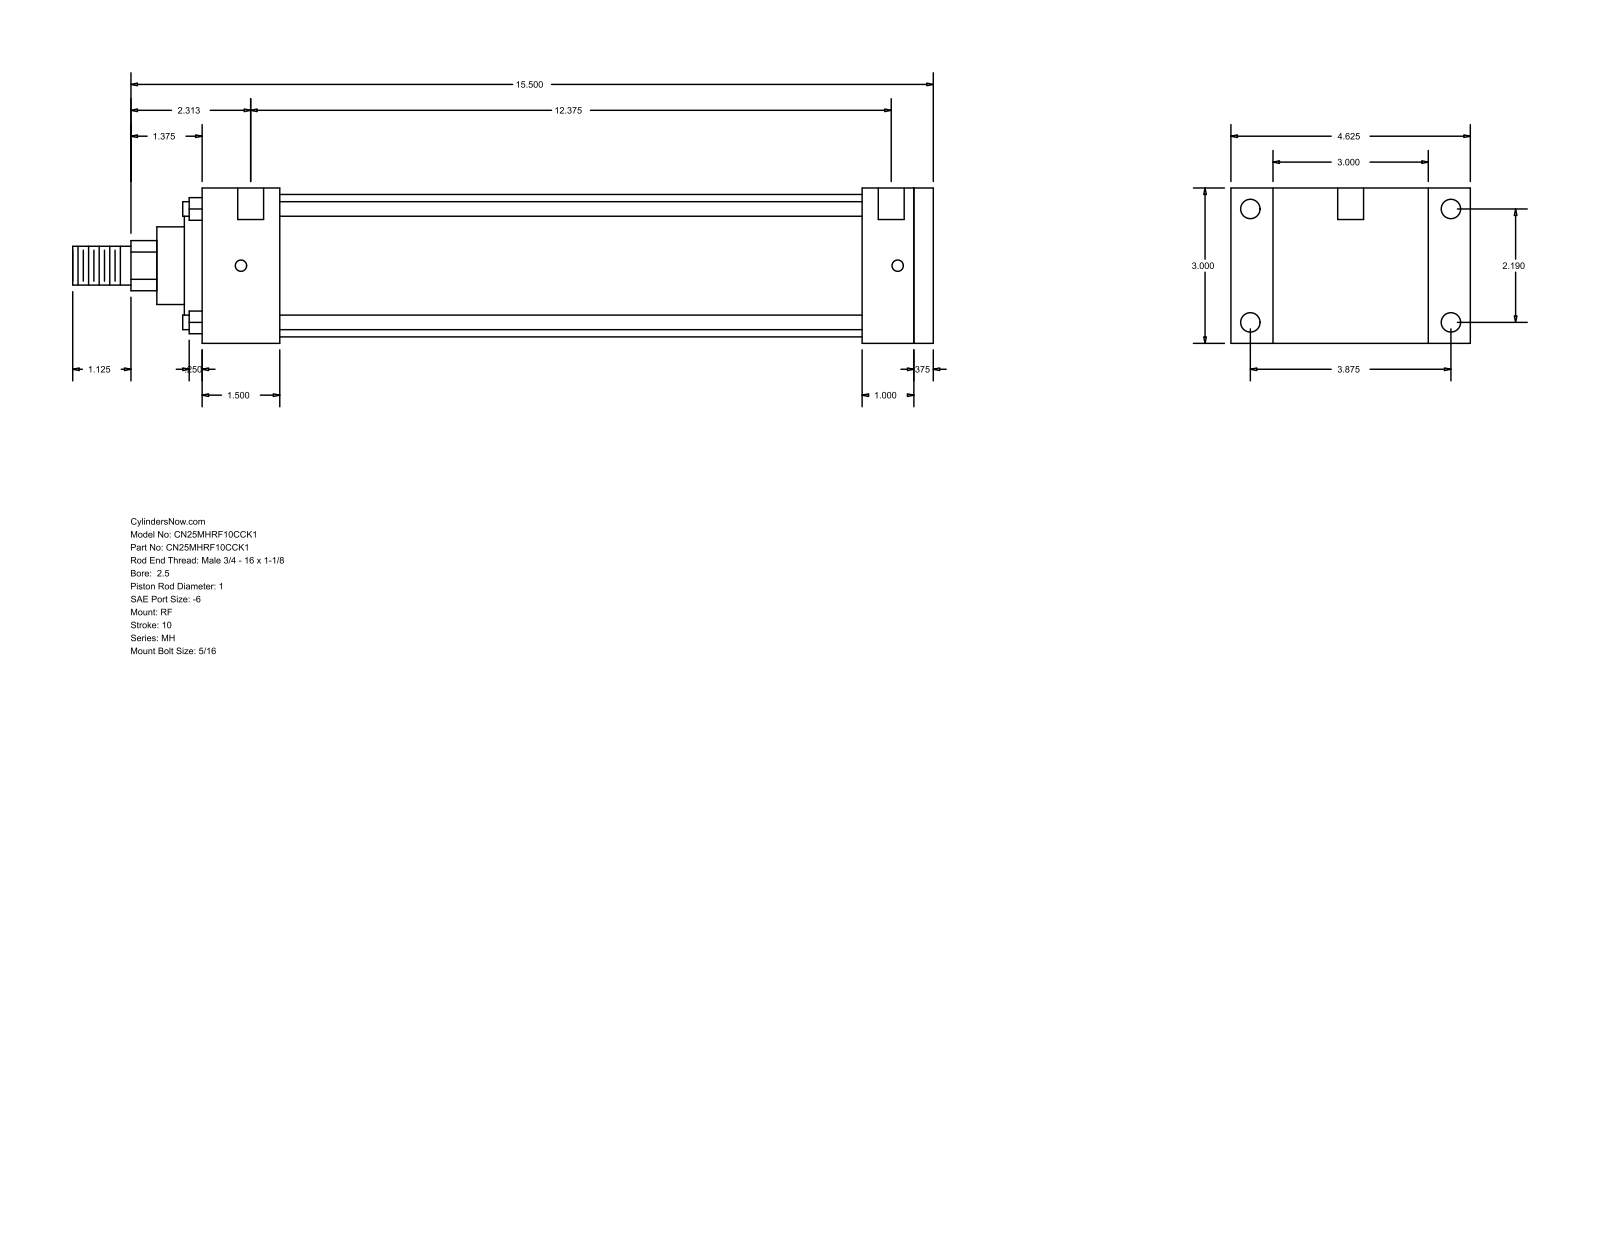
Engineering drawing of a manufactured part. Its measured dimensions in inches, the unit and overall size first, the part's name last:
Units: inches
Overall size (bounding box): 16.625 × 4.625 × 3
Round holes (diameter × count): ⌀0.219 ×4, ⌀0.375 ×4, ⌀0.5 ×2
Round bosses / shafts (diameter × count): ⌀0.281 ×4, ⌀2.75 ×1, ⌀2.375 ×1, ⌀1.5 ×1, ⌀1 ×1, ⌀0.75 ×1
Partial cylindrical surfaces — rounded edges, fillets, slot ends (radius × count): R0.484 ×1
Main face-to-face distances: 3, 0.375, 14.125, 13.75, 12.75, 1, 1.375, 1.5, 11.25, 12.25
Hole centre spacings: 2.19, 3.875, 4.451, 12.687, 0.125, 0.187, 12.375, 12.5
Bodies: 0 solids, 94 faces (65 planar, 29 cylindrical, 0 other)
Part name (STEP PRODUCT): MH_RF__0250_1
STEP written by: GSSL Pune (CONFIG_CONTROL_DESIGN)
